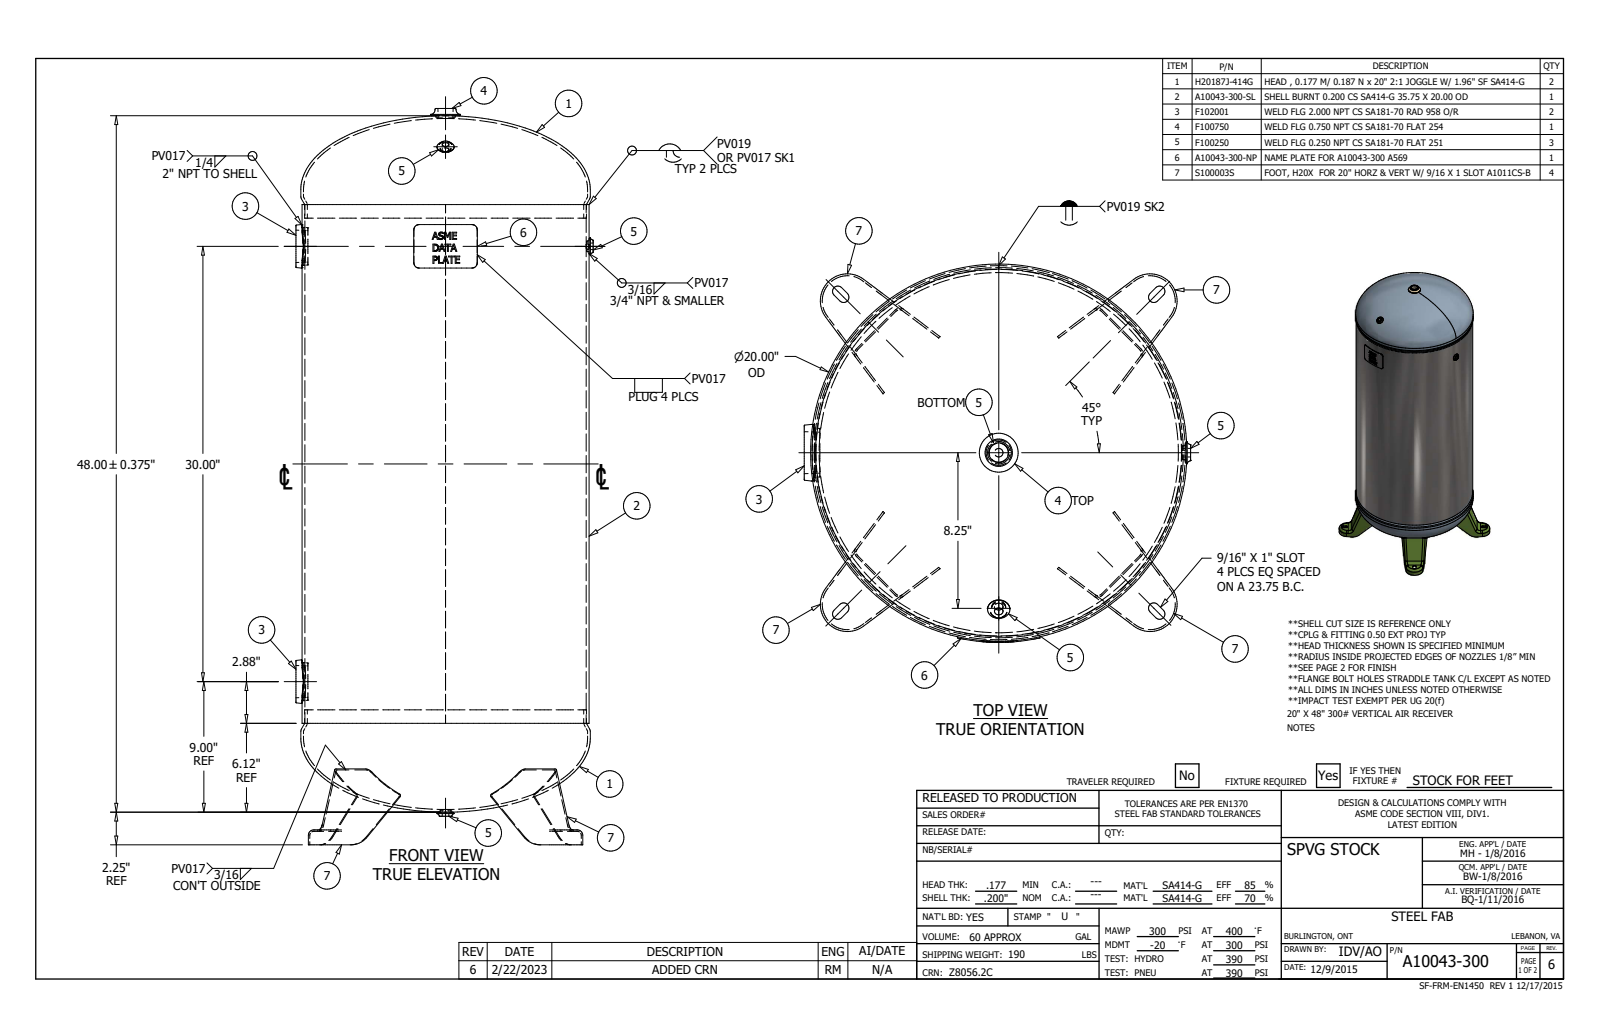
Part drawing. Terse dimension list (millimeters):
name: A10043-300; A10043-300-SL; H20187J-414G; F102001 (+4 more)
written by: Autodesk Inventor 2019 (AUTOMOTIVE_DESIGN)
unit: mm
bodies: 20 solids, 430 faces (200 planar, 120 cylindrical, 110 other)
size: 1288.9 × 521.6 × 509.5
volume: 10 950 000 mm³; area: 4 586 000 mm²
holes: 3× ⌀11.5, 2× ⌀50.8, 2× ⌀55.2, 1× ⌀6.4, 1× ⌀485, 1× ⌀493.5, 1× ⌀498.5, 1× ⌀508
bosses: 2× ⌀76.2, 2× ⌀66.7, 1× ⌀503.7, 1× ⌀494.5, 1× ⌀52.4, 1× ⌀36.9
rounds: 20× R9.5, 16× R7, 8× R7.1, 4× R3.2, 4× R15.9, 4× R18.4, 4× R34, 4× R36.5
face distances: 2.5, 2.5, 152.3, 152.2, 23.7, 884.3, 154.8, 154.7, 149.8, 149.7
hole spacings: 762
